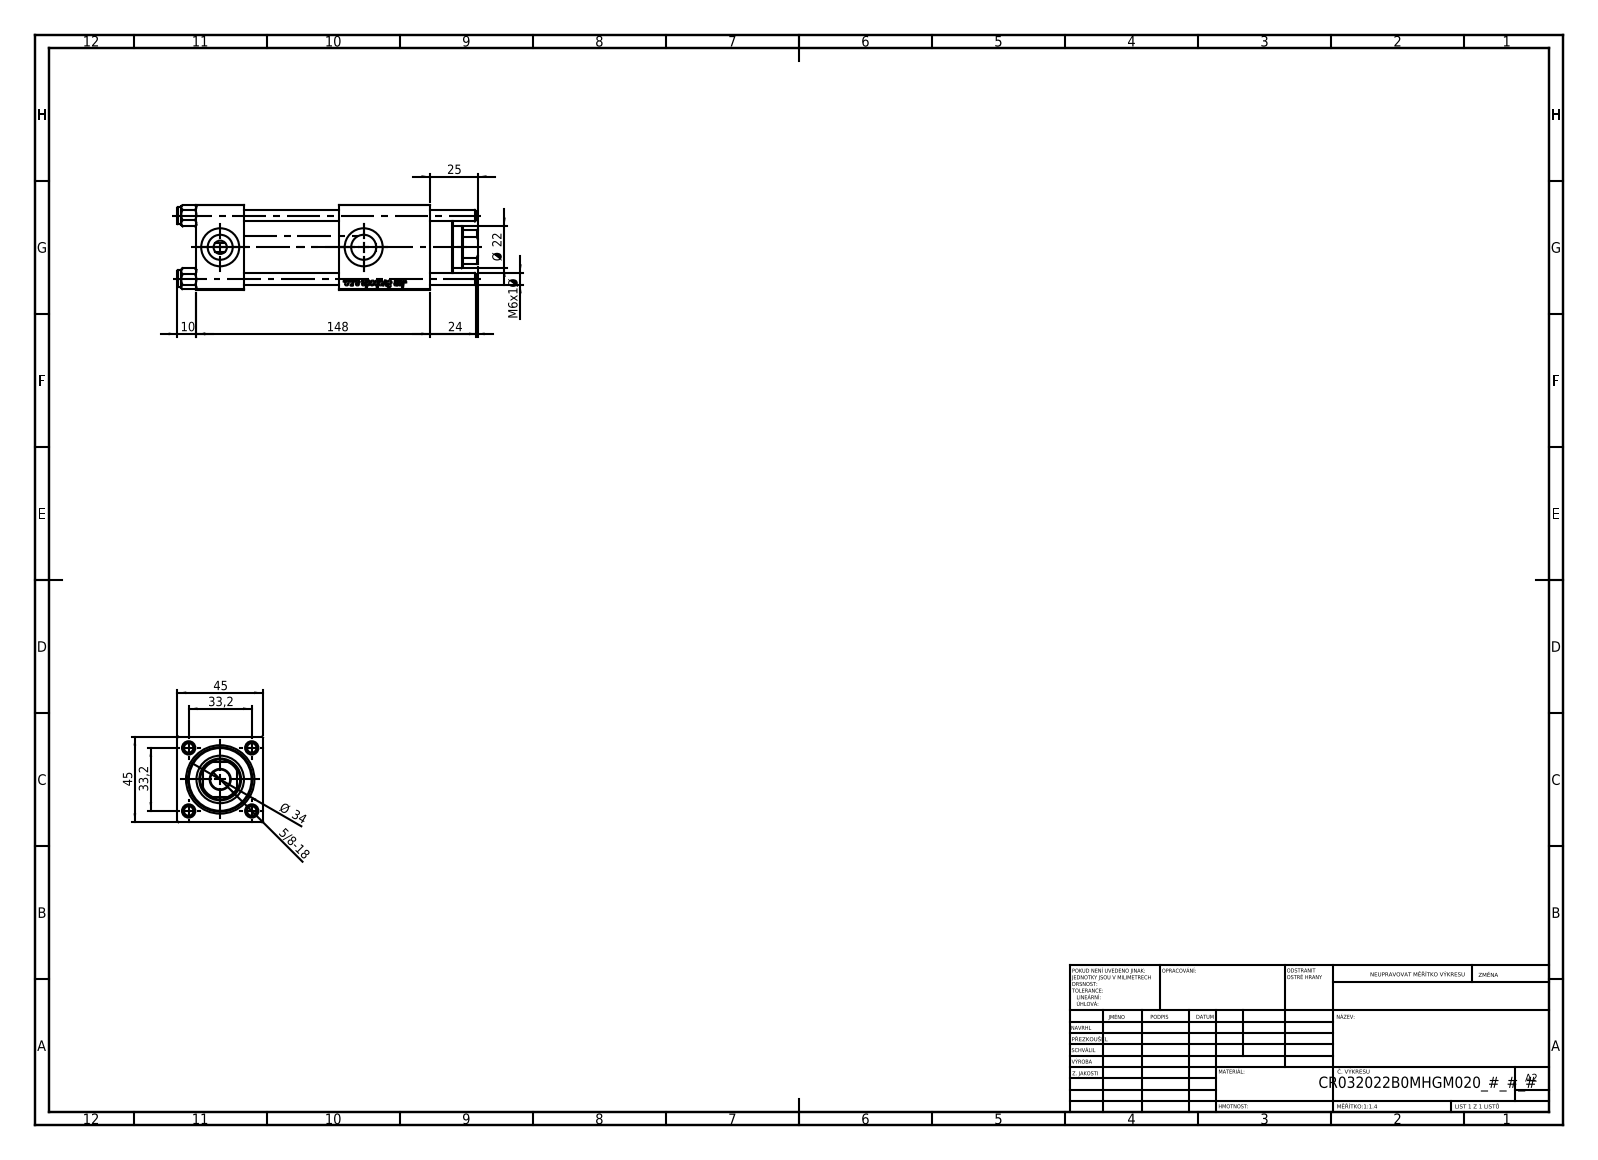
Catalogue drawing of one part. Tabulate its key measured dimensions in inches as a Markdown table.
| quantity | value |
| --- | --- |
| part name | V215_VC_A; NUT_M5_B; V215CR_VCP_B; V215CR_B-1 (+1 more) |
| STEP written by | SolidWorks 2019 (CONFIG_CONTROL_DESIGN) |
| units | inches |
| bodies | 11 solids, 1157 faces (431 planar, 78 cylindrical, 648 other) |
| overall size | 6.22 × 1.772 × 1.772 |
| volume | 13.08 in³ |
| surface area | 119 in² |
| round holes (diameter × count) | 0.236 × 4, 0.276 × 2, 0.518 × 2, 0.787 × 2, 0.413 × 1, 0.866 × 1, 0.945 × 1, 0.984 × 1, 1.26 × 1, 1.299 × 1 |
| round bosses / shafts (diameter × count) | 0.354 × 4, 1.496 × 1, 1.339 × 1 |
| partial cylindrical surfaces (radius × count) | 0.413 × 1 |
| main face-to-face distances | 1.772, 0.984, 1.969, 4.843, 2.953, 3.858, 1.89, 3.713, 2.728, 0.76 |
| hole center spacings | 0.924, 1.307, 1.848, 2.972 |
